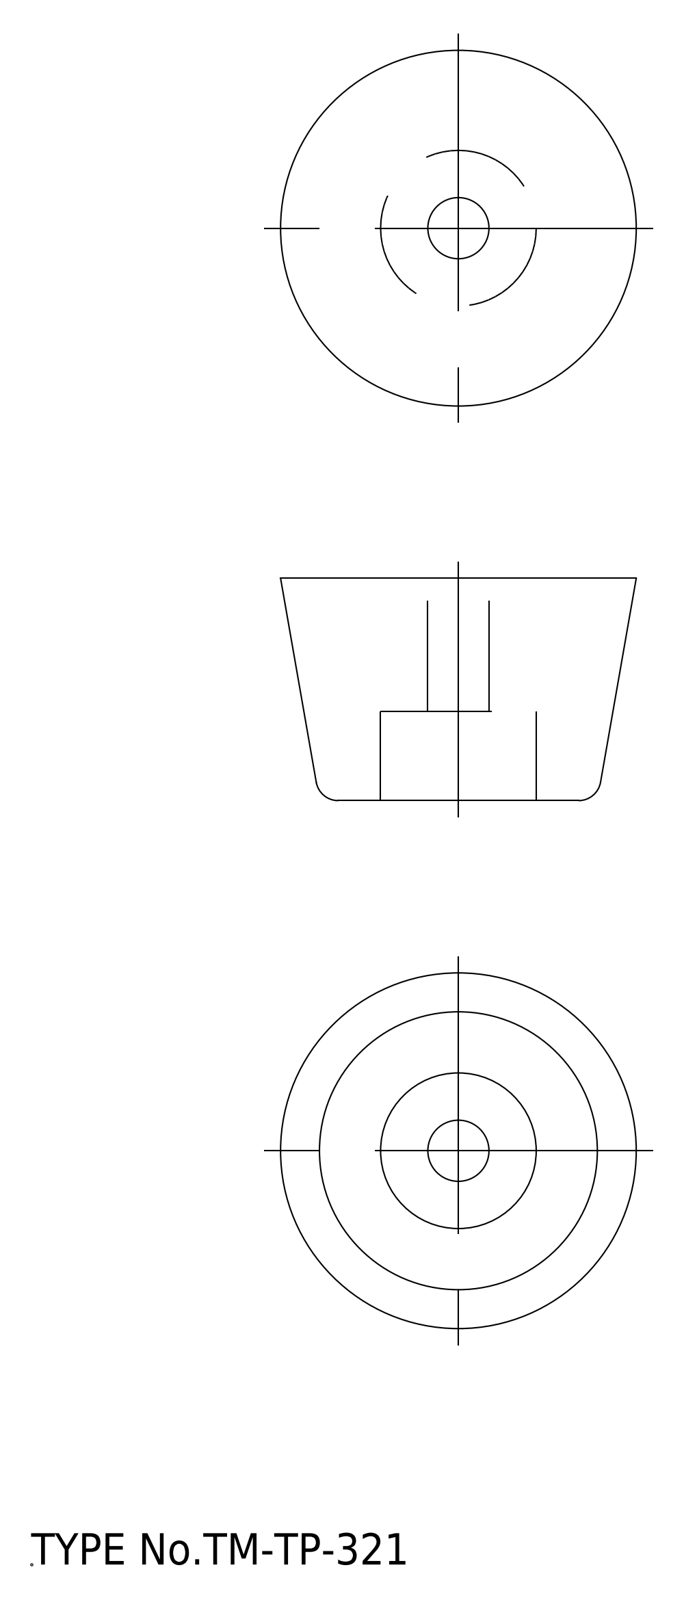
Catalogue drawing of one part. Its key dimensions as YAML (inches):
step_written_by: "spGate 19.8.4 (****-****-****-****) (AUTOMOTIVE_DESIGN)"
units: inches
bodies: {solids: 1, faces: 11, planar: 3, cylindrical: 4, other: 4}
overall_size: [1.26, 1.26, 0.787]
volume: 0.689
surface_area: 5.552
round_holes:
  - {diameter: 0.217, count: 1}
  - {diameter: 0.551, count: 1}
face_to_face_distances: [0.787, 0.315, 0.472]
